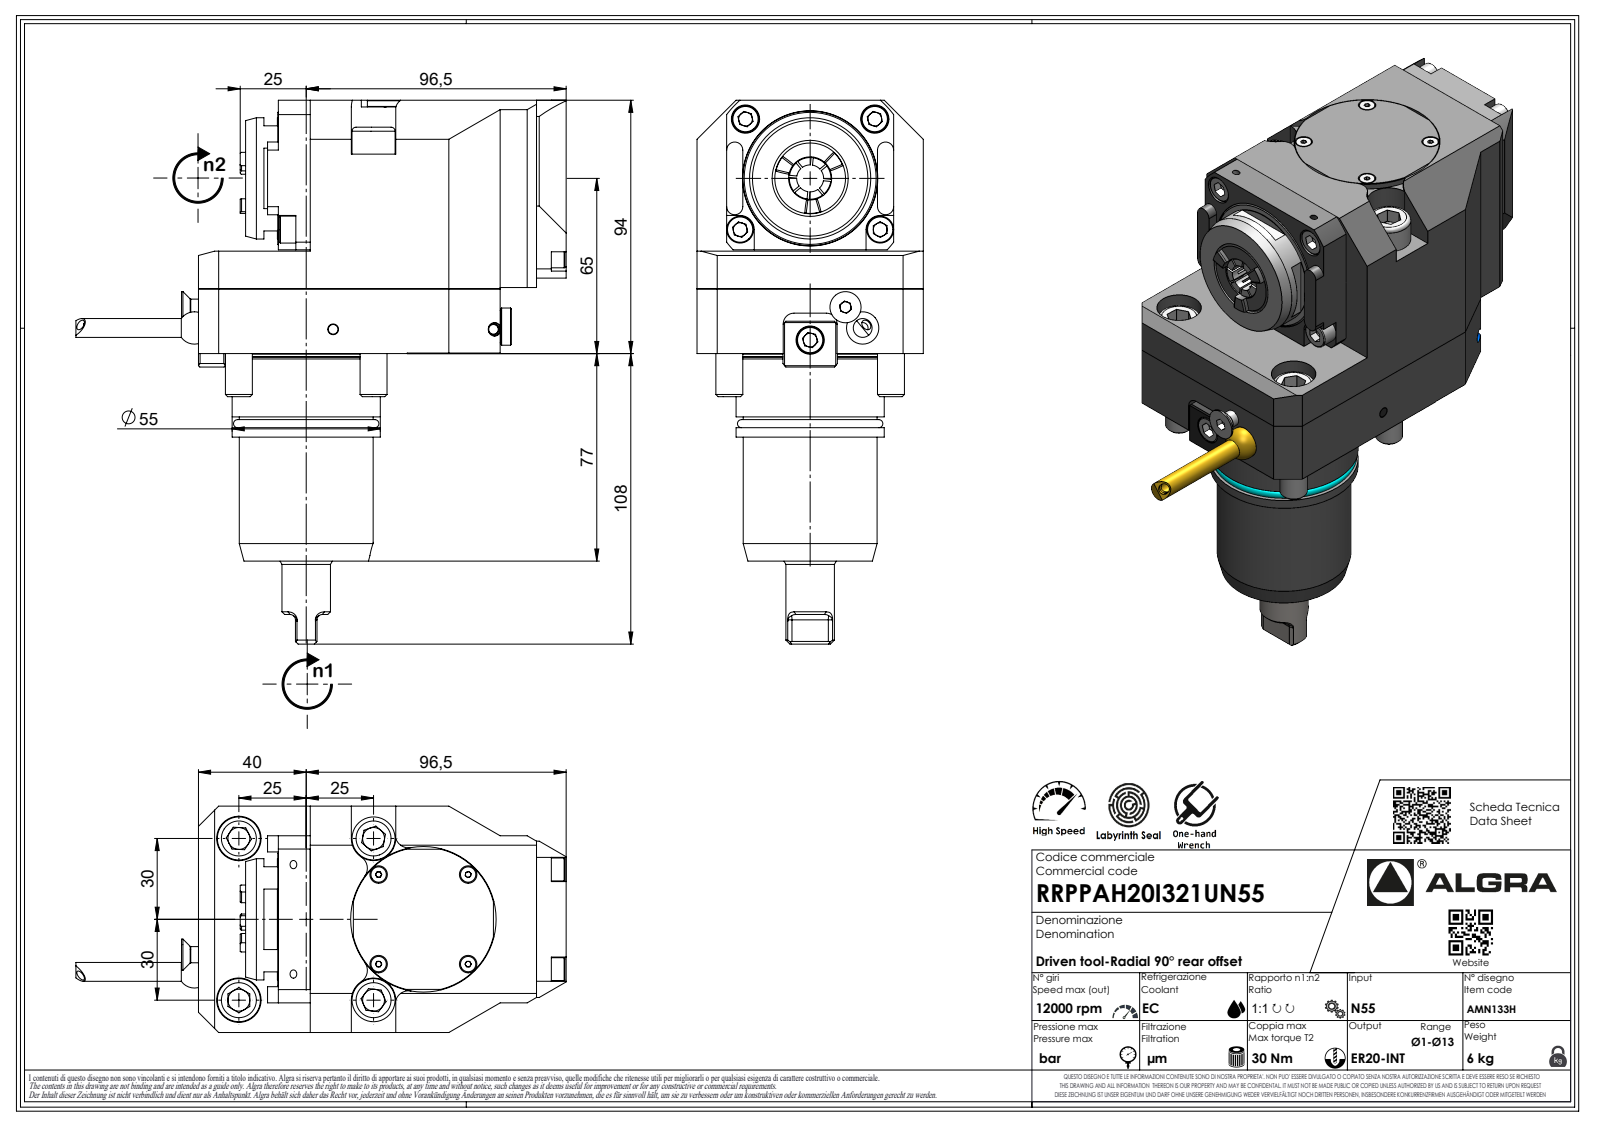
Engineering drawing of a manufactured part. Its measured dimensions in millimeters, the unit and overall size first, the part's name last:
Units: millimetres
Overall size (bounding box): 201.8 × 182 × 84
Round holes (diameter × count): ⌀4 ×2, ⌀2.1 ×1, ⌀46.2 ×1, ⌀50.2 ×1
Round bosses / shafts (diameter × count): ⌀10 ×4, ⌀55 ×1, ⌀54.6 ×1, ⌀50 ×1, ⌀49.7 ×1, ⌀46 ×1, ⌀45 ×1, ⌀18 ×1
Partial cylindrical surfaces — rounded edges, fillets, slot ends (radius × count): R2 ×8, R0.33 ×7, R0.52 ×7, R3.7 ×7, R3 ×4, R4 ×2, R5 ×2, R8 ×2
Main face-to-face distances: 84, 11, 94, 56, 38, 73, 37.8, 93.8, 136.5, 24.5
Volume: 980 306 mm³ · Surface area: 81 303 mm²
Bodies: 1 solid, 531 faces (331 planar, 83 cylindrical, 117 other)
Part name (STEP PRODUCT): RRPPAH20I321UN55
STEP written by: SolidWorks 2023 (AUTOMOTIVE_DESIGN)
